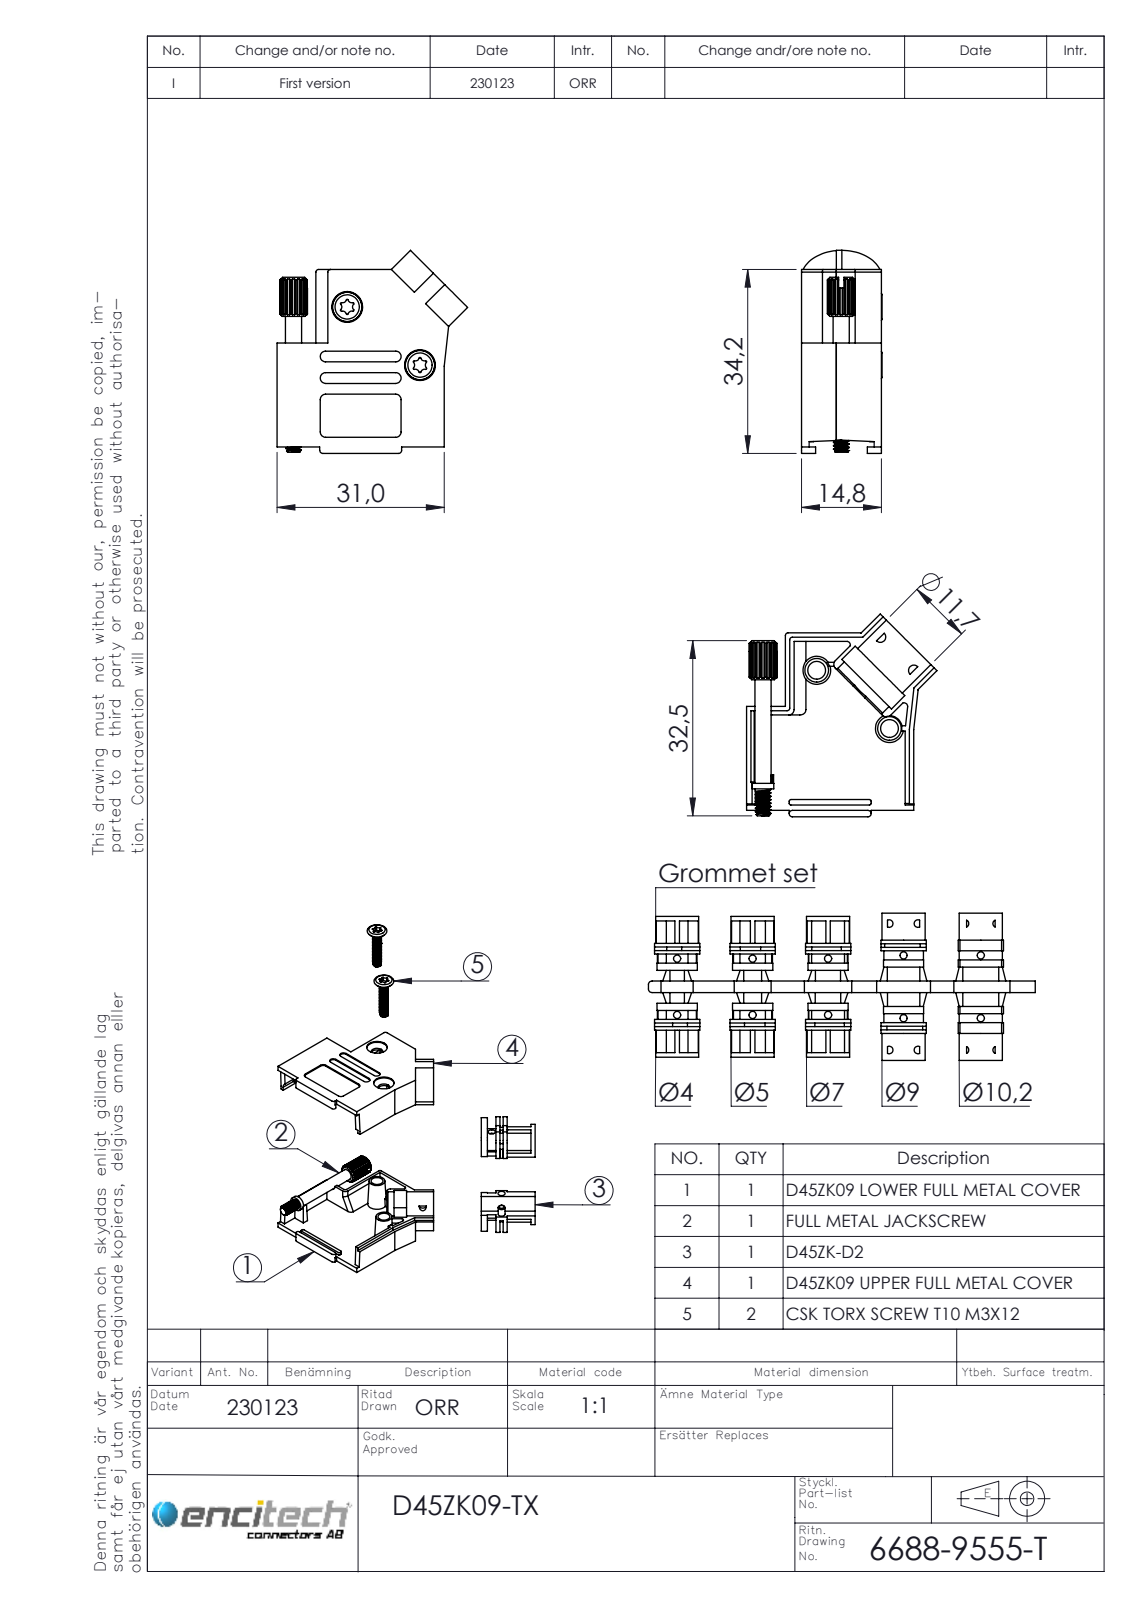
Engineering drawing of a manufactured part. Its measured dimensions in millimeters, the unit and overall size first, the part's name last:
Units: millimetres
Overall size (bounding box): 37.7 × 35.35 × 14.9
Round holes (diameter × count): ⌀2 ×3, ⌀3.3 ×2, ⌀5.7 ×2, ⌀7 ×1
Round bosses / shafts (diameter × count): ⌀2.5 ×2, ⌀1.9 ×2, ⌀11.6 ×1, ⌀9.2 ×1, ⌀4 ×1, ⌀3 ×1, ⌀2.85 ×1
Partial cylindrical surfaces — rounded edges, fillets, slot ends (radius × count): R1 ×20, R0.5 ×13, R0.18 ×12, R0.7 ×12, R0.3 ×4, R5.91 ×4, R0.6 ×2, R1.65 ×2
Main face-to-face distances: 1.4, 14.8, 13.4, 13.45, 12.05, 1.35, 1.6, 14.5, 29.4, 7.45
Hole centre spacings: 5.71, 5.87, 7.22, 8.97, 9.13, 10, 14.51, 14.82
Volume: 5 934 mm³ · Surface area: 9 602 mm²
Bodies: 7 solids, 643 faces (315 planar, 263 cylindrical, 65 other)
Part name (STEP PRODUCT): 6855-0117-12; 6688-9555-T; 6826-0141-01; 6805-0106-01 (+2 more)
STEP written by: SolidWorks 2021 (AUTOMOTIVE_DESIGN)
